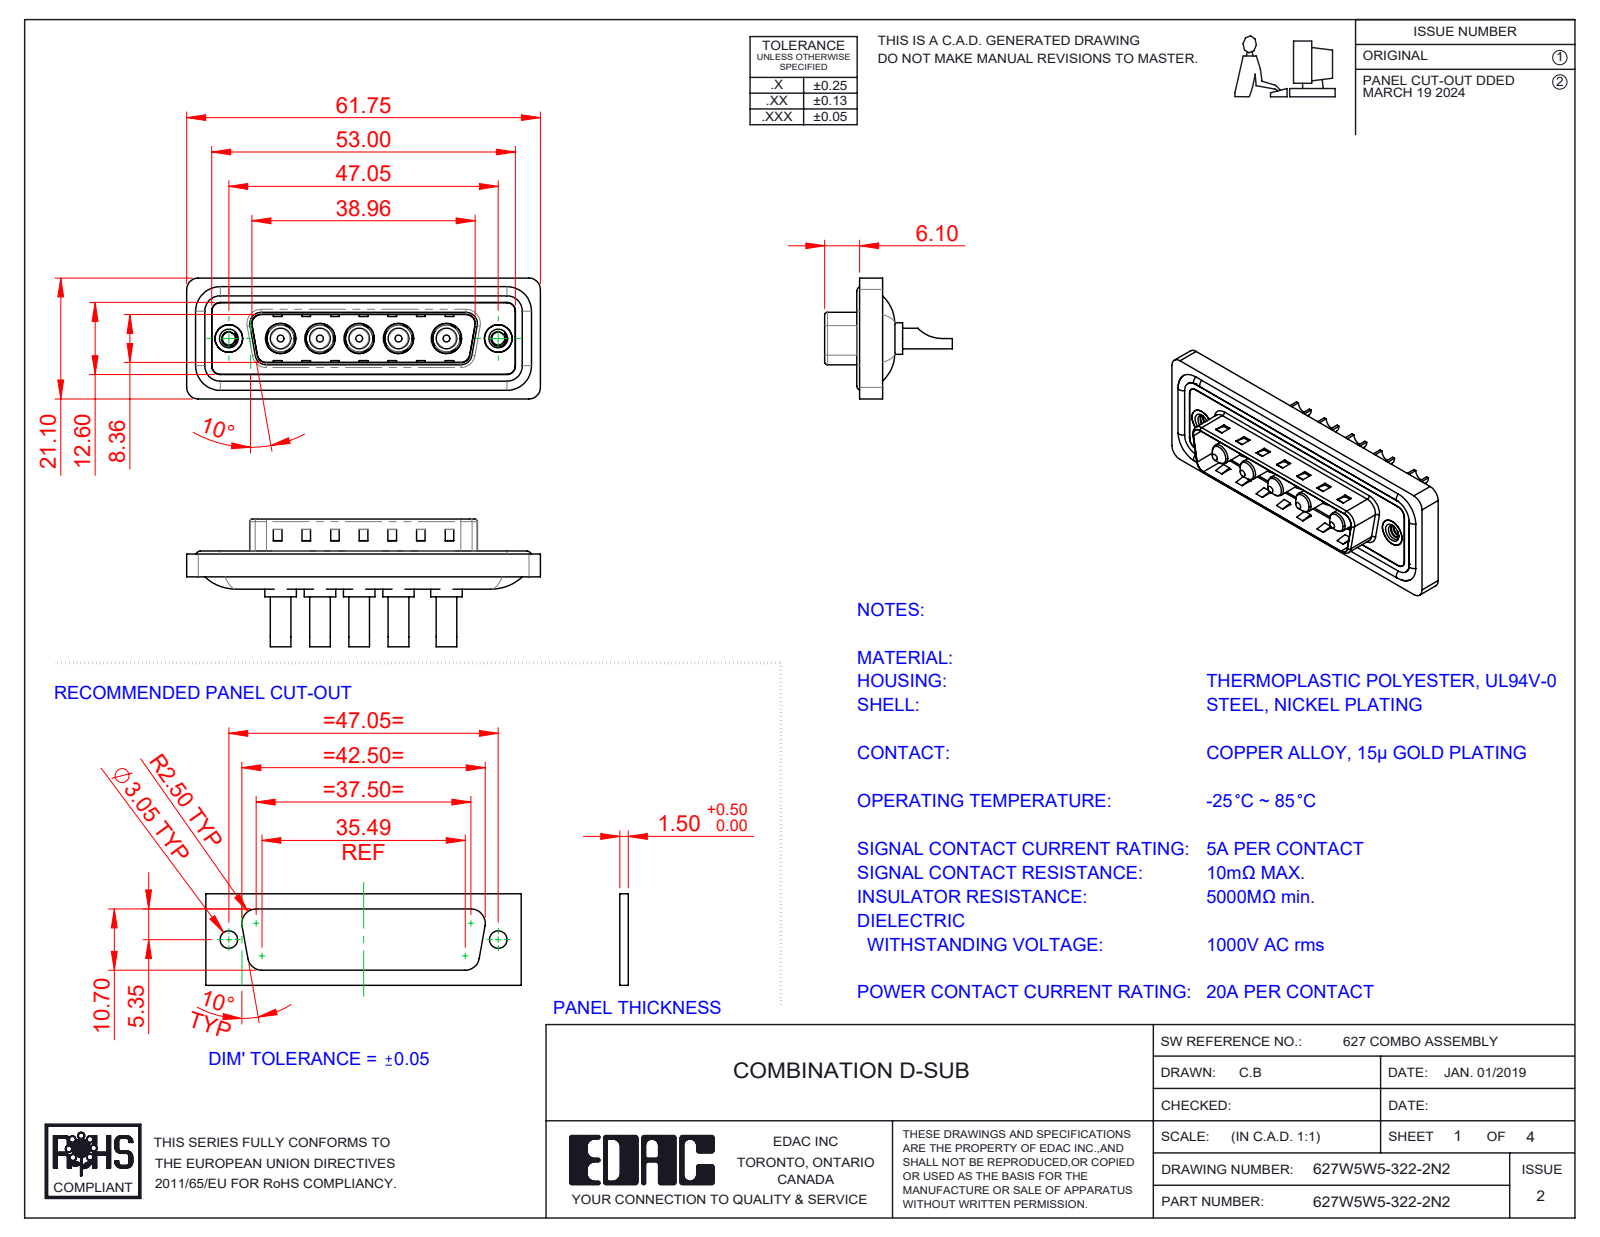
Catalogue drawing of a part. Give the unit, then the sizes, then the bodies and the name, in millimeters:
Units: millimetres
Overall size (bounding box): 61.75 × 22.3 × 21.1
Round holes (diameter × count): ⌀2.7 ×5, ⌀4.85 ×5, ⌀5.3 ×5, ⌀2.26 ×2, ⌀4 ×2, ⌀4.8 ×2, ⌀5 ×2
Round bosses / shafts (diameter × count): ⌀5.5 ×5, ⌀5.2 ×5, ⌀4.75 ×5, ⌀3.75 ×5, ⌀3.6 ×5, ⌀1.6 ×4, ⌀4.9 ×2
Partial cylindrical surfaces — rounded edges, fillets, slot ends (radius × count): R1.5 ×22, R2 ×18, R0.5 ×8, R1.6 ×8, R2.1 ×5, R0.25 ×4, R0.6 ×4, R0.65 ×4
Main face-to-face distances: 0.4, 1.5, 0.5, 1.1, 3.1, 1.6, 2.9, 0.82, 9.58, 5.65
Hole centre spacings: 6.86, 9.04, 13.73, 38.01, 6.87, 8.37, 8.38, 9.05
Volume: 7 537 mm³ · Surface area: 12 208 mm²
Bodies: 17 solids, 713 faces (274 planar, 298 cylindrical, 141 other)
Part name (STEP PRODUCT): 627Combo Shell Front_25 Contacts; 627Combo Threaded Rivet_2; 627Combo Waterproof Housing_25 Contacts; 627Combo Housing_5W5 (+3 more)
STEP written by: SolidWorks 2023 (CONFIG_CONTROL_DESIGN)
